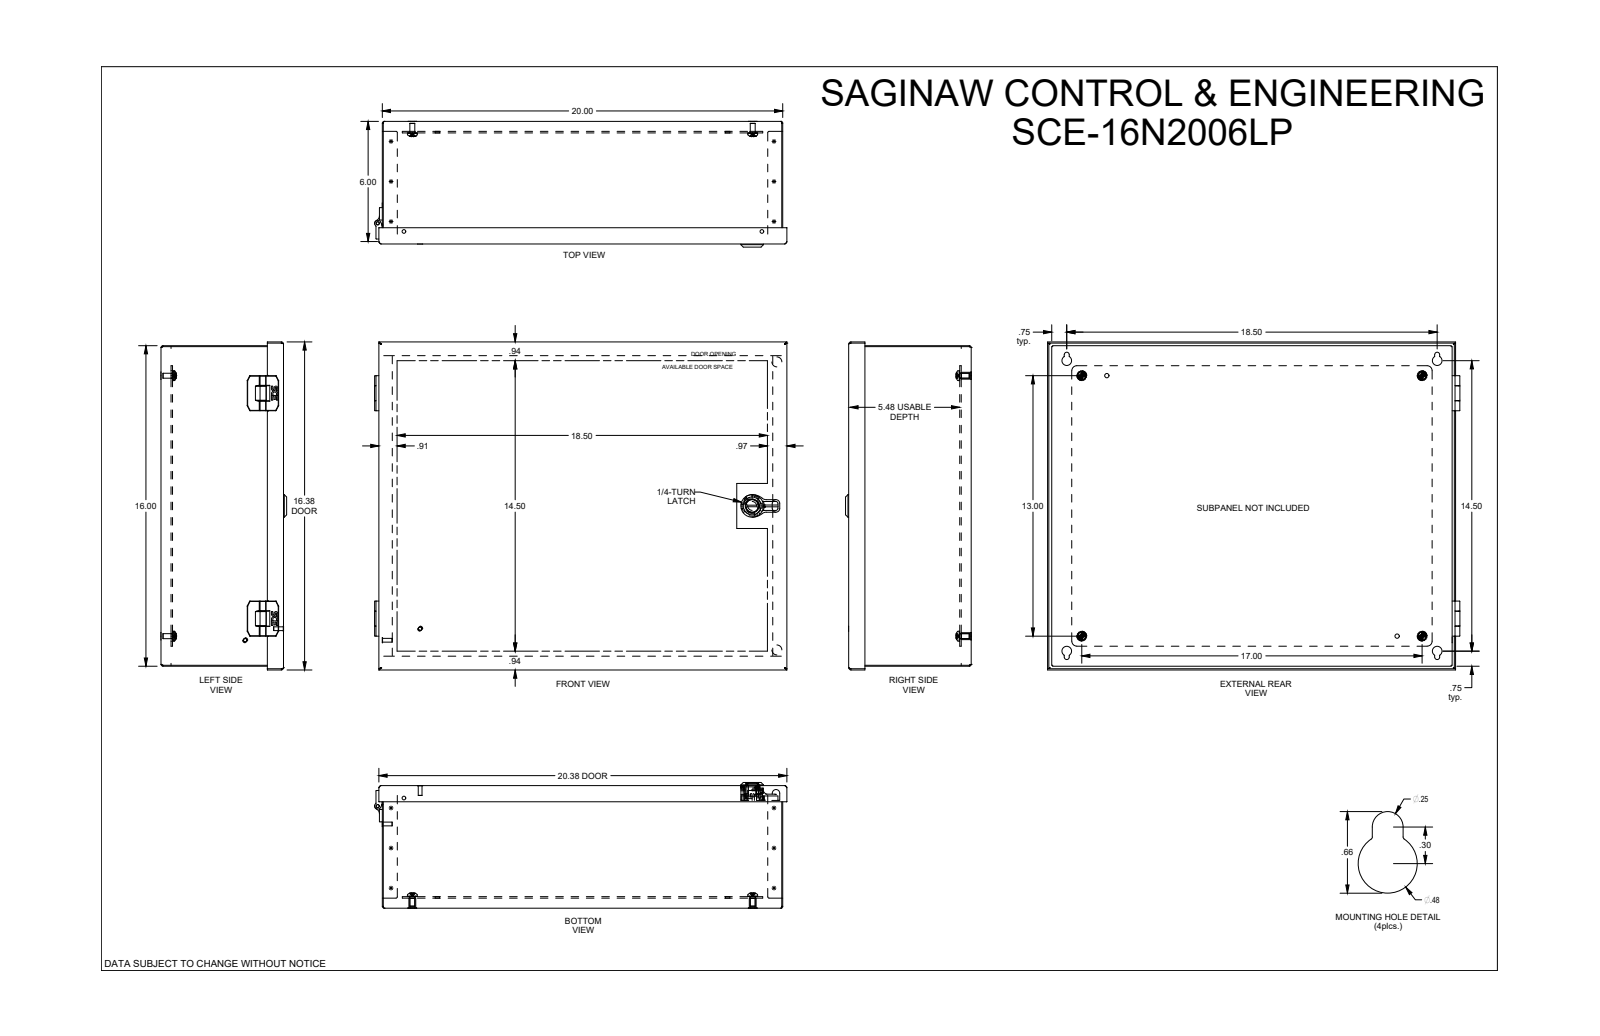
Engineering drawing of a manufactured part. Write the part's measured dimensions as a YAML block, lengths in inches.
part_name: "SCE-16N2006LP"
step_written_by: "SolidWorks 2019 (AUTOMOTIVE_DESIGN)"
units: inches
bodies: {solids: 31, faces: 1543, planar: 578, cylindrical: 641, other: 324}
overall_size: [20.593, 16.375, 6.279]
volume: 90.42
surface_area: 2885
round_holes:
  - {diameter: 0.17, count: 4}
  - {diameter: 0.25, count: 4}
  - {diameter: 0.281, count: 4}
  - {diameter: 0.329, count: 4}
  - {diameter: 0.343, count: 4}
  - {diameter: 0.48, count: 4}
  - {diameter: 0.193, count: 3}
  - {diameter: 0.218, count: 2}
  - {diameter: 0.158, count: 1}
  - {diameter: 0.44, count: 1}
  - {diameter: 0.635, count: 1}
  - {diameter: 0.891, count: 1}
round_bosses_or_shafts:
  - {diameter: 0.492, count: 4}
  - {diameter: 0.479, count: 4}
  - {diameter: 0.341, count: 4}
  - {diameter: 0.248, count: 4}
  - {diameter: 0.237, count: 4}
  - {diameter: 0.16, count: 4}
  - {diameter: 0.5, count: 2}
  - {diameter: 0.323, count: 2}
partial_cylinders:
  - {radius: 0.01, count: 253}
  - {radius: 0.02, count: 95}
  - {radius: 0.06, count: 25}
  - {radius: 0.015, count: 24}
  - {radius: 0.025, count: 24}
  - {radius: 0.055, count: 6}
  - {radius: 0.25, count: 6}
  - {radius: 0.125, count: 4}
face_to_face_distances: [0.06, 6.059, 5.999, 6.119, 0.5, 0.44, 0.575, 0.515, 5.484, 5.544]
hole_center_spacings: [1.061, 13.77, 17.766, 22.453, 1.091, 1.102, 11.25, 0.555]
